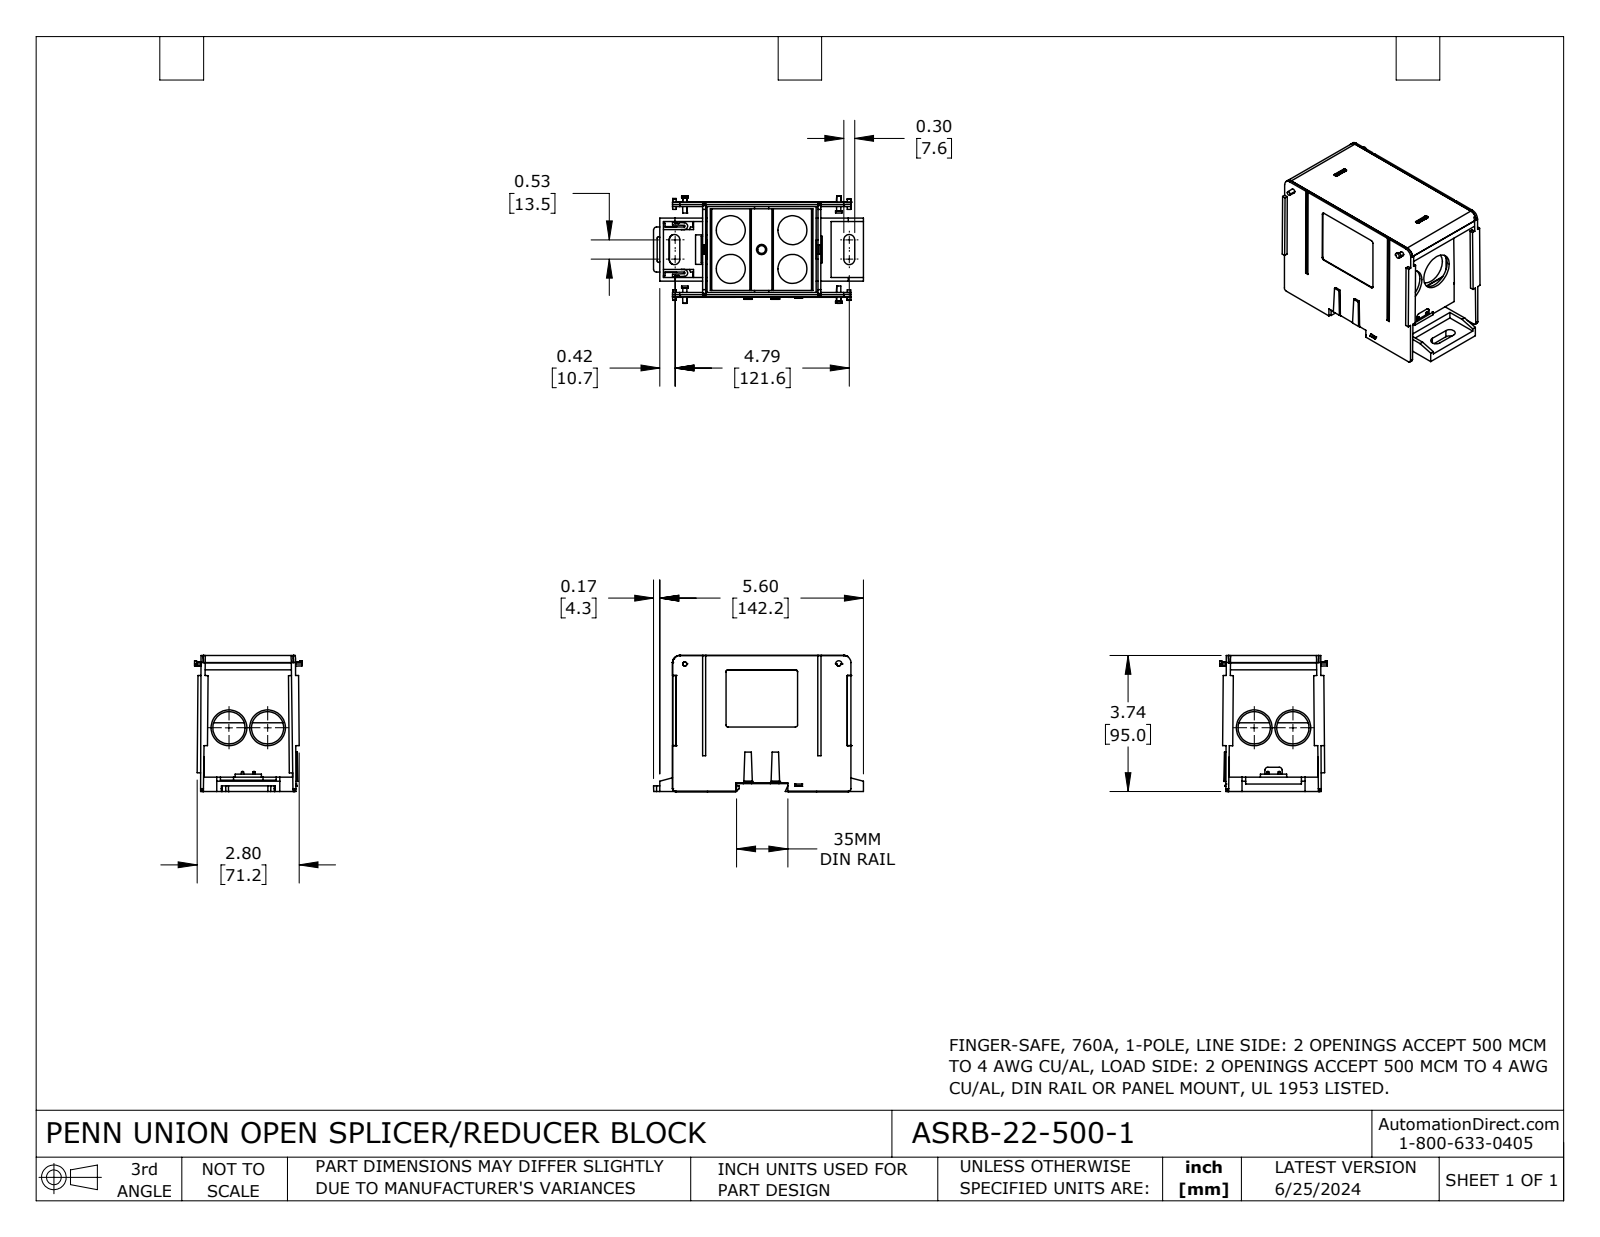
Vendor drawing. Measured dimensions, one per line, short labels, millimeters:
name: ASRB-22-500-1
written by: SolidWorks 2023 (CONFIG_CONTROL_DESIGN)
unit: mm
bodies: 10 solids, 779 faces (551 planar, 157 cylindrical, 71 other)
size: 146.6 × 95 × 75.1
volume: 302 000 mm³; area: 151 200 mm²
holes: 4× ⌀20.3, 2× ⌀22.5, 2× ⌀25, 1× ⌀5.4, 1× ⌀7.1
rounds: 26× R1, 18× R1.5, 16× R0.5, 10× R2, 10× R5, 6× R0.3, 4× R2.3, 4× R3.8
face distances: 2, 80.5, 64.5, 3.3, 1.8, 62.7, 0.5, 82.5, 78.5, 30.5
hole spacings: 25.4, 27, 43.1, 50.9
